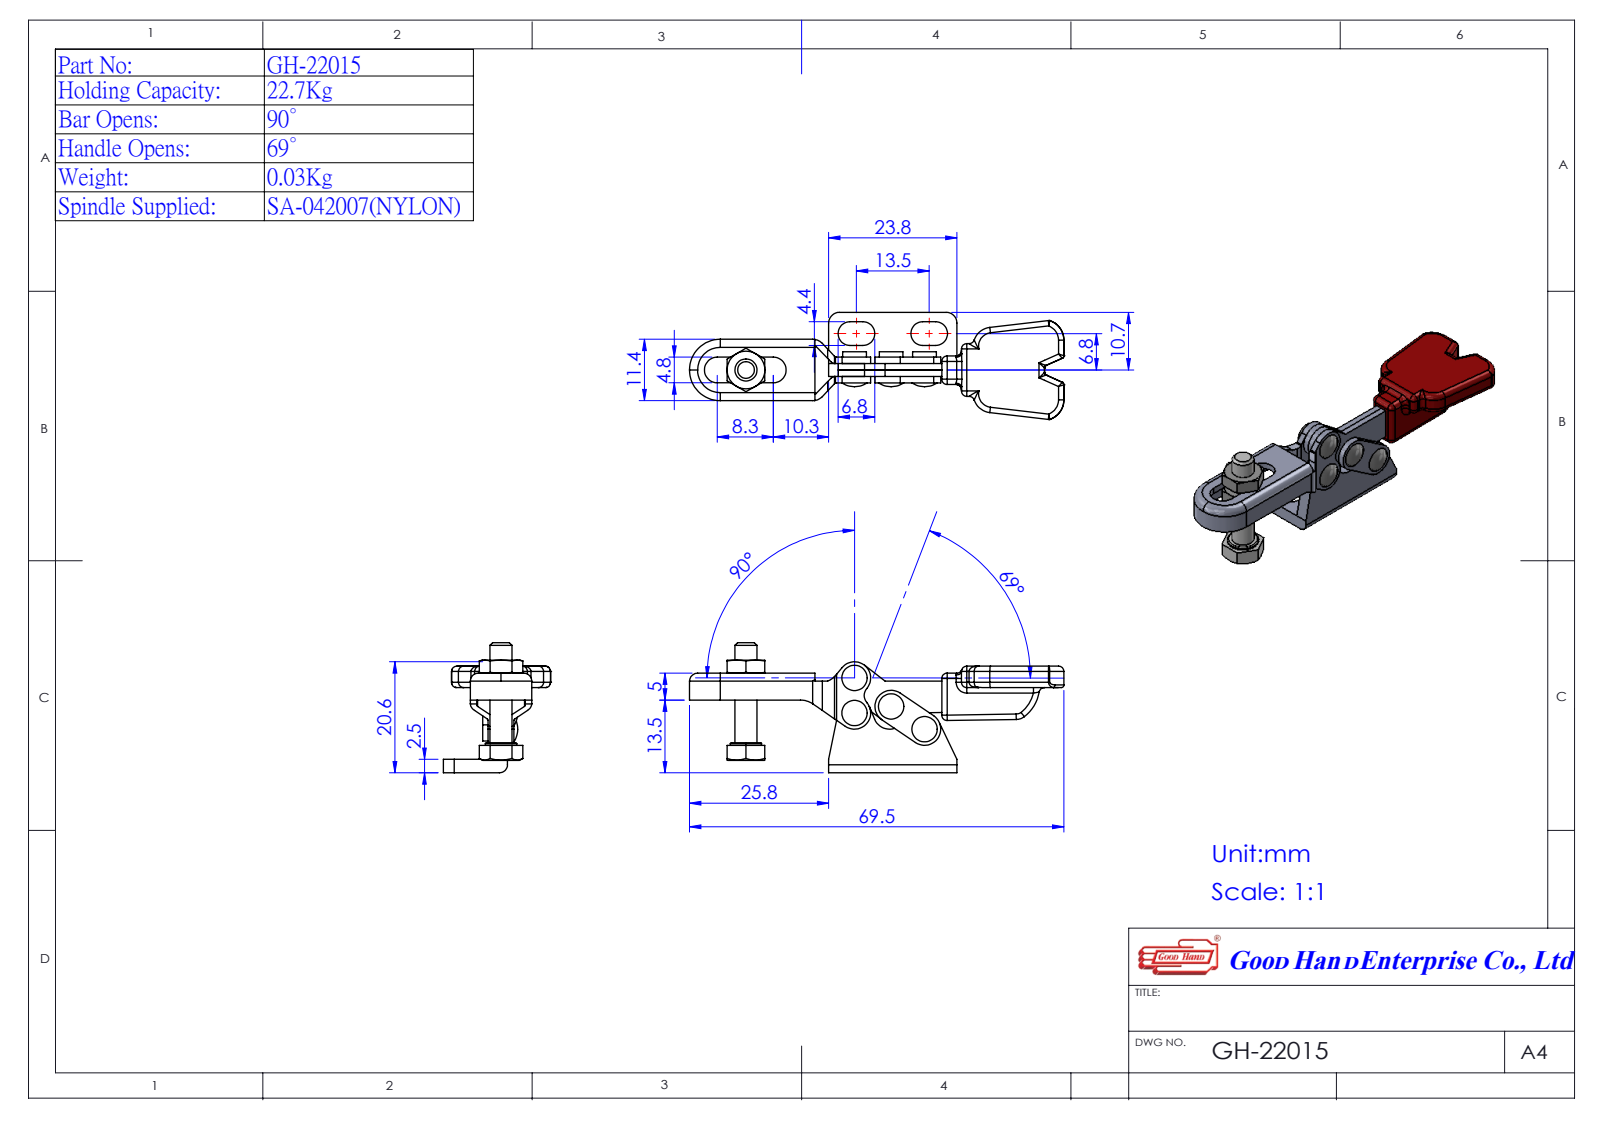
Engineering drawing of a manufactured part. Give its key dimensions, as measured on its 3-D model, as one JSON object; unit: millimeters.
{"part_name": "Group3^GH-22015(簡化); 12200501-1^GH-22015(簡化); Group2^GH-22015(簡化); Group5^GH-22015(簡化) (+2 more)", "step_written_by": "SolidWorks 2016 (AUTOMOTIVE_DESIGN)", "units": "millimeters", "bodies": {"solids": 5, "faces": 278, "planar": 117, "cylindrical": 113, "other": 48}, "overall_size": [69.5, 25.6, 19.89], "volume_mm3": 4504, "surface_area_mm2": 5283, "round_holes": [[2, 4]], "round_bosses_or_shafts": [[3.5, 4], [6, 1], [5.8, 1], [4.1, 1]], "partial_cylinders_radius": [[1, 20], [0.5, 5], [3, 5], [2, 4], [2.2, 4], [2.5, 3], [2.38, 2], [3.5, 2]], "face_to_face_distances": [1.2, 2.4, 2.5, 17.3, 4.5, 5.7, 6.9, 3.3, 1.5, 2.7], "hole_center_spacings": [6.5, 6.91, 7.49, 8.62, 13.34, 16.1]}
